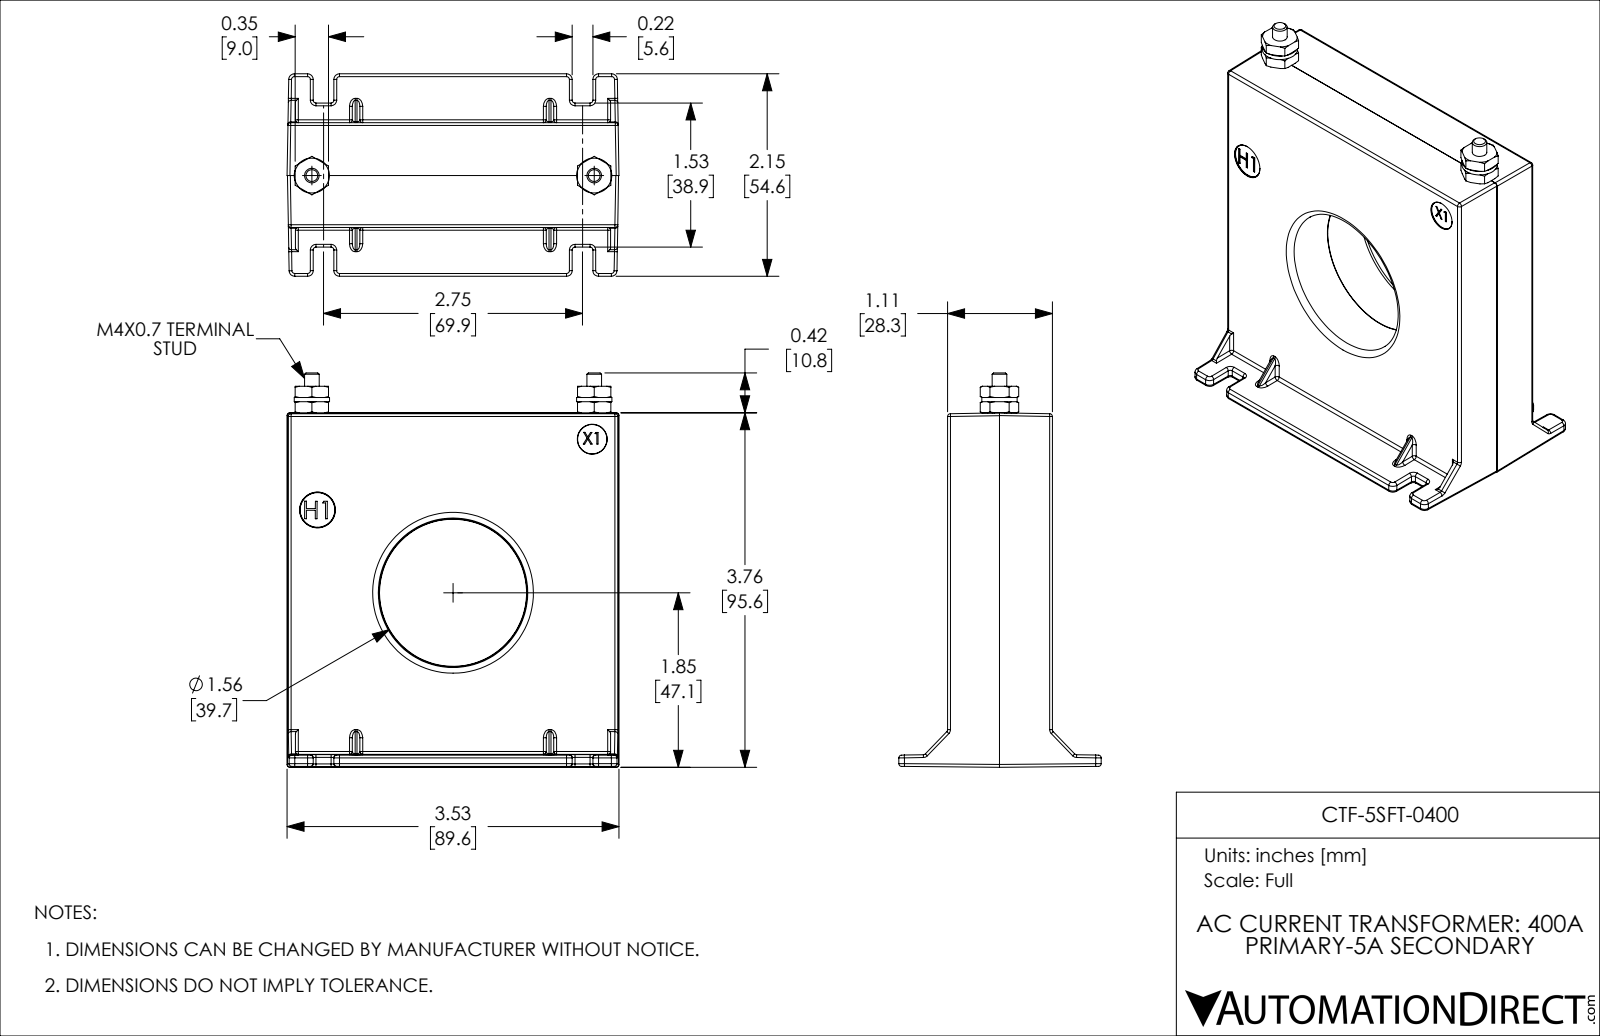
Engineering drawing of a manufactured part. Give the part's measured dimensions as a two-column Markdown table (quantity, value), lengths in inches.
| quantity | value |
| --- | --- |
| part name | CTF-5SFT-0400 |
| STEP written by | SolidWorks 2018 (AUTOMOTIVE_DESIGN) |
| units | inches |
| bodies | 10 solids, 437 faces (134 planar, 156 cylindrical, 147 other) |
| overall size | 4.188 × 3.527 × 2.15 |
| volume | 13.01 in³ |
| surface area | 75.78 in² |
| round holes (diameter × count) | 0.155 × 2, 0.165 × 2, 0.155 × 1, 0.312 × 1, 0.375 × 1 |
| round bosses / shafts (diameter × count) | 0.375 × 2 |
| partial cylindrical surfaces (radius × count) | 0.03 × 92, 0.06 × 12 |
| main face-to-face distances | 0.562, 1.113, 0.551, 3.523, 3.616, 0.163, 0.045, 0.118, 0.519, 1.632 |
| hole center spacings | 3, 3.015 |
